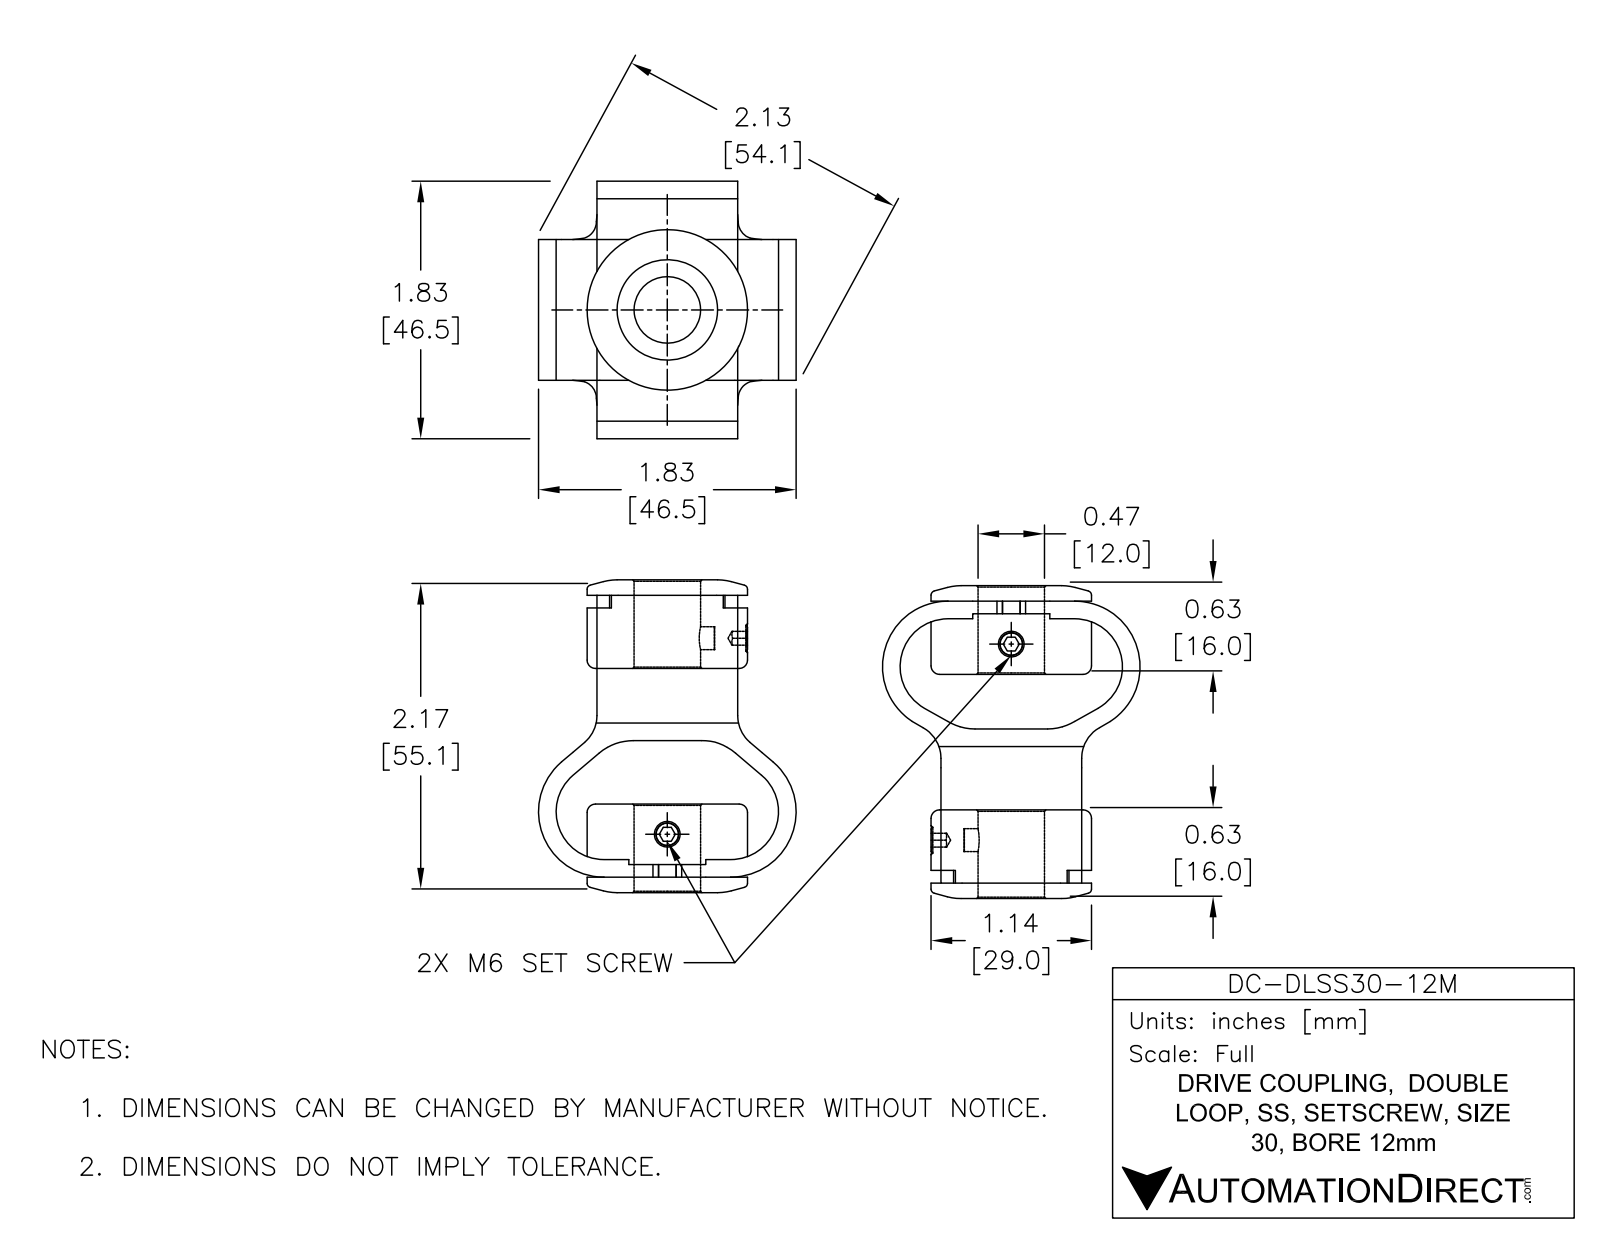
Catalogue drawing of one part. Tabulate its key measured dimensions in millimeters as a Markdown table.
| quantity | value |
| --- | --- |
| part name | DC-DLSS30-12M |
| STEP written by | SolidWorks 2015 (AUTOMOTIVE_DESIGN) |
| units | millimeters |
| bodies | 1 solid, 169 faces (92 planar, 37 cylindrical, 40 other) |
| overall size | 56.46 × 46.48 × 46.48 |
| volume | 28 704 mm³ |
| surface area | 15 050 mm² |
| round holes (diameter × count) | 5.26 × 2, 12 × 1 |
| round bosses / shafts (diameter × count) | 28.96 × 1 |
| partial cylindrical surfaces (radius × count) | 8.64 × 4, 9.53 × 4, 11.81 × 4, 10.41 × 1 |
| main face-to-face distances | 25.4, 24.46, 3.17, 14.61, 9.85, 11.44, 13.02, 16, 40.46, 24.64 |
